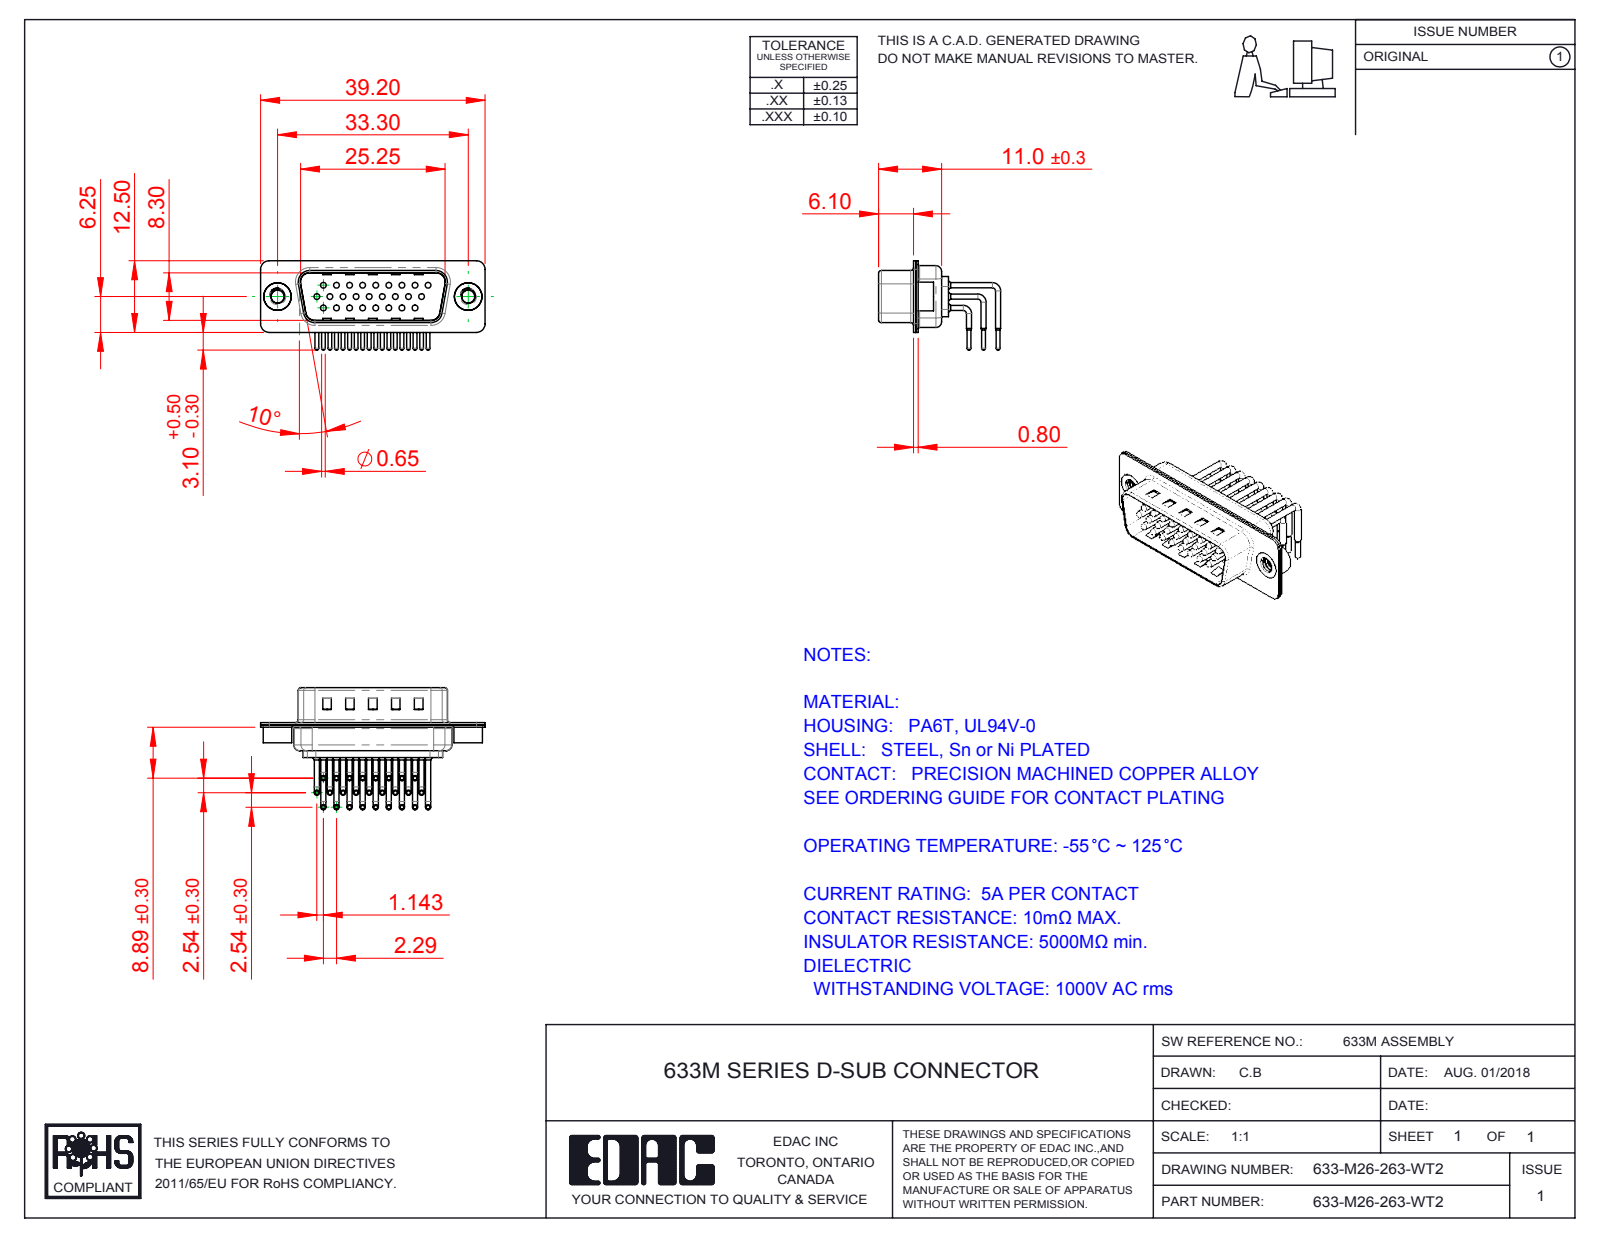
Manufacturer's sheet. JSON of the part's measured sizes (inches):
{"part_name": "633M 4-40 Threaded Rivet; 633-M26-263-WT2; 633M Shell Front_26 Contacts; 633M Contact Row 1 (+4 more)", "step_written_by": "SolidWorks 2016 (CONFIG_CONTROL_DESIGN)", "units": "inches", "bodies": {"solids": 31, "faces": 3200, "planar": 1803, "cylindrical": 1069, "other": 328}, "overall_size": [1.543, 0.839, 0.614], "volume_in3": 0.128, "surface_area_in2": 10.38, "round_holes": [[0.039, 26], [0.067, 26], [0.079, 26], [0.089, 2], [0.157, 2], [0.189, 2]], "round_bosses_or_shafts": [[0.035, 52], [0.059, 26], [0.026, 26], [0.197, 2], [0.193, 2]], "partial_cylinders_radius": [[0.04, 26], [0.059, 16], [0.079, 12], [0.02, 8], [0.063, 8], [0.01, 4], [0.024, 4], [0.026, 4]], "face_to_face_distances": [0.016, 0.033, 0.376, 0.059, 0.343, 0.075, 0.049, 0.409, 0.031, 0.014], "hole_center_spacings": [0.156, 0.09, 0.18, 0.238, 0.09, 0.324, 0.27, 0.413]}
